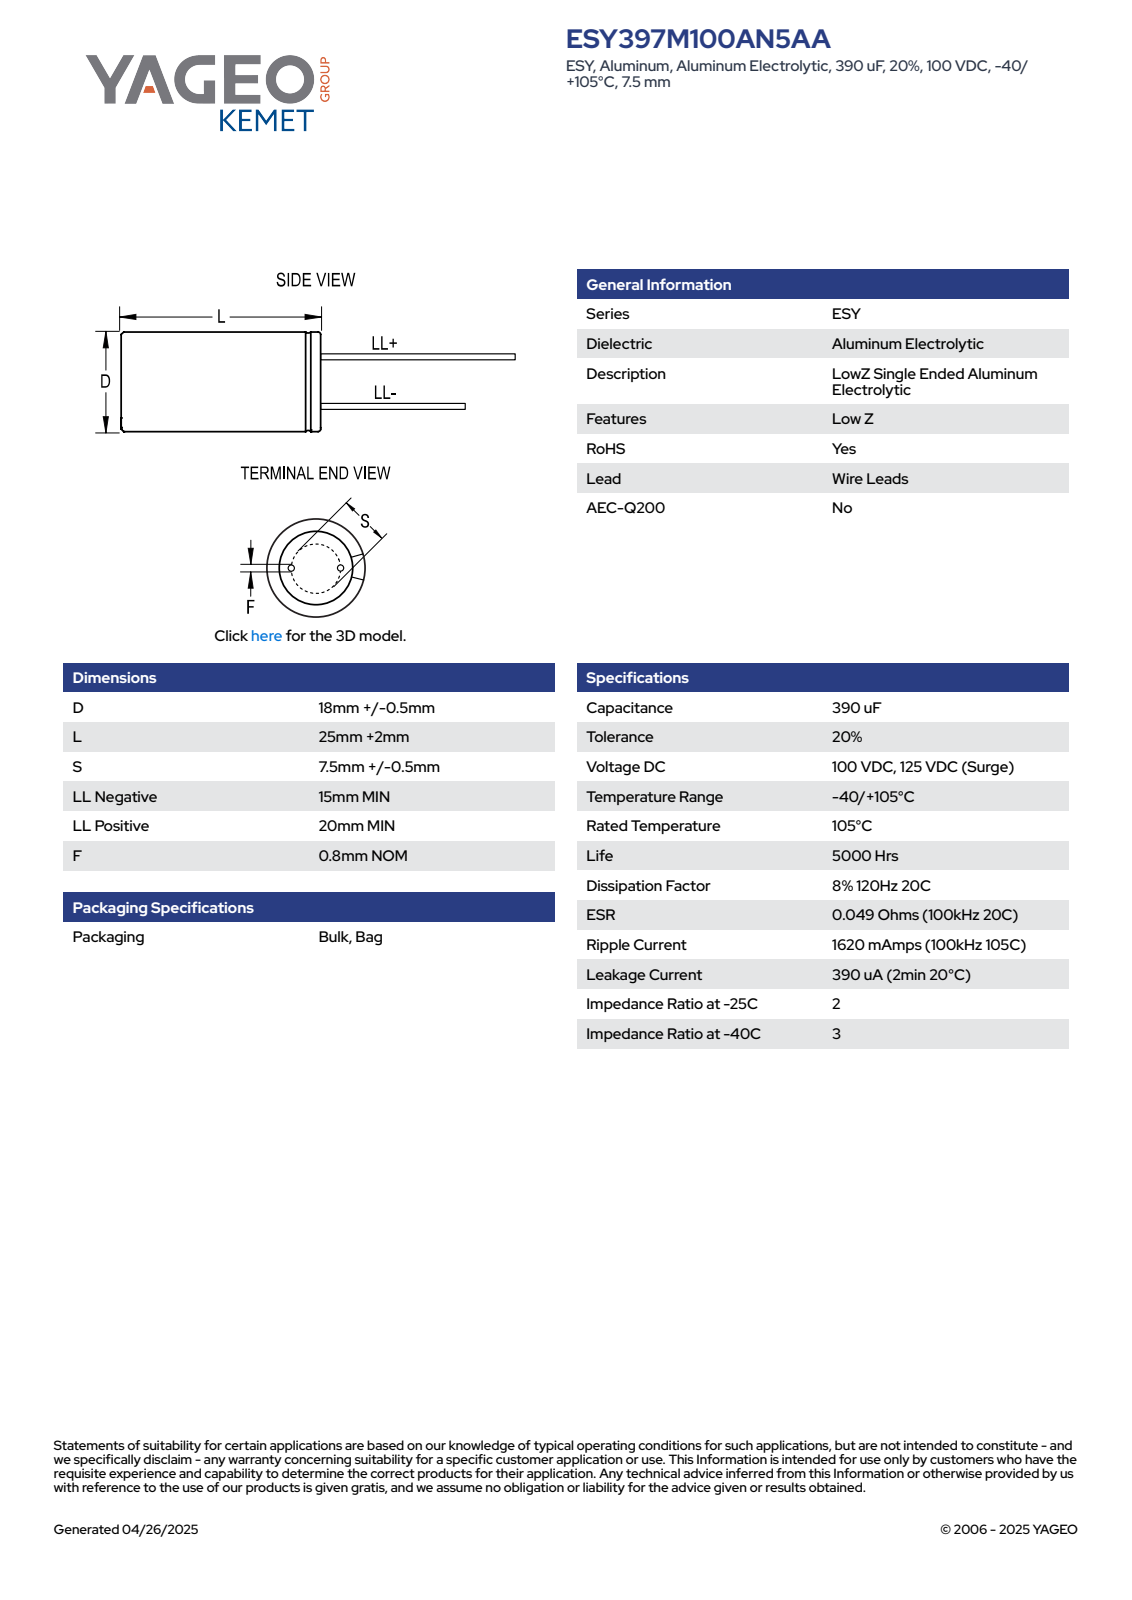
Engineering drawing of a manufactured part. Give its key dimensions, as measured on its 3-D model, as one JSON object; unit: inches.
{"part_name": "CAR_KLP_18X25_D18.5L27S7.5F0.8", "step_written_by": "SolidWorks 2014 (AUTOMOTIVE_DESIGN)", "units": "inches", "bodies": {"solids": 4, "faces": 75, "planar": 61, "cylindrical": 8, "other": 6}, "overall_size": [1.851, 0.728, 0.728], "volume_in3": 0.44, "surface_area_in2": 3.526, "round_bosses_or_shafts": [[0.031, 2], [0.728, 1]], "face_to_face_distances": [1.063, 1.063, 1.654, 1.851, 1.654, 1.85, 0.591, 0.787, 0.197, 0.098]}
